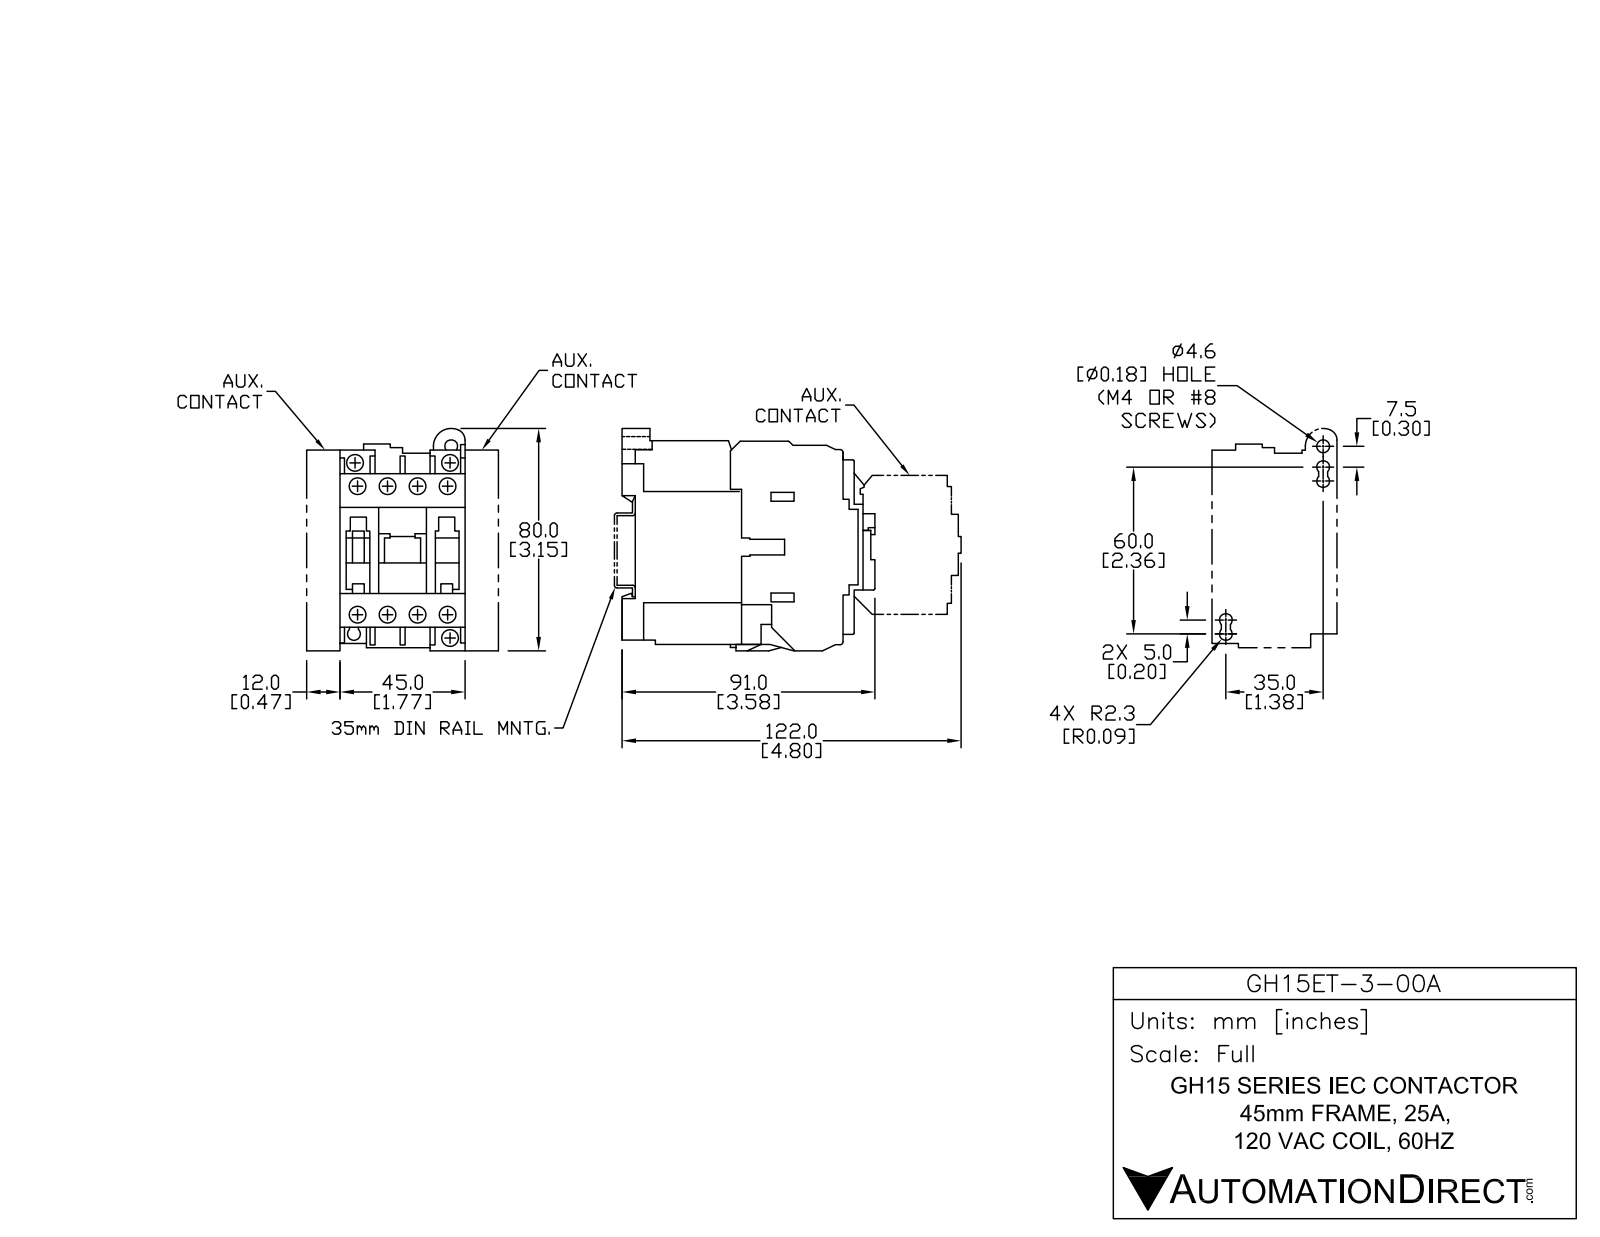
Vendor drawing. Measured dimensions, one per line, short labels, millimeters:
name: GH15ET-3-00A
written by: SolidWorks 2009 (AUTOMOTIVE_DESIGN)
unit: mm
bodies: 1 solid, 678 faces (481 planar, 51 cylindrical, 146 other)
size: 91.5 × 80 × 45
volume: 218 393 mm³; area: 38 409 mm²
holes: 6× ⌀7, 3× ⌀6.25, 1× ⌀4.6
rounds: 9× R1, 8× R2.3, 2× R3, 1× R4.99, 1× R5
face distances: 45, 15, 7.75, 35.5, 14, 1, 9.5, 43.25, 54, 1.75
hole spacings: 14.5, 55.91, 54, 29, 61.29, 4.67, 5.04, 5.89
